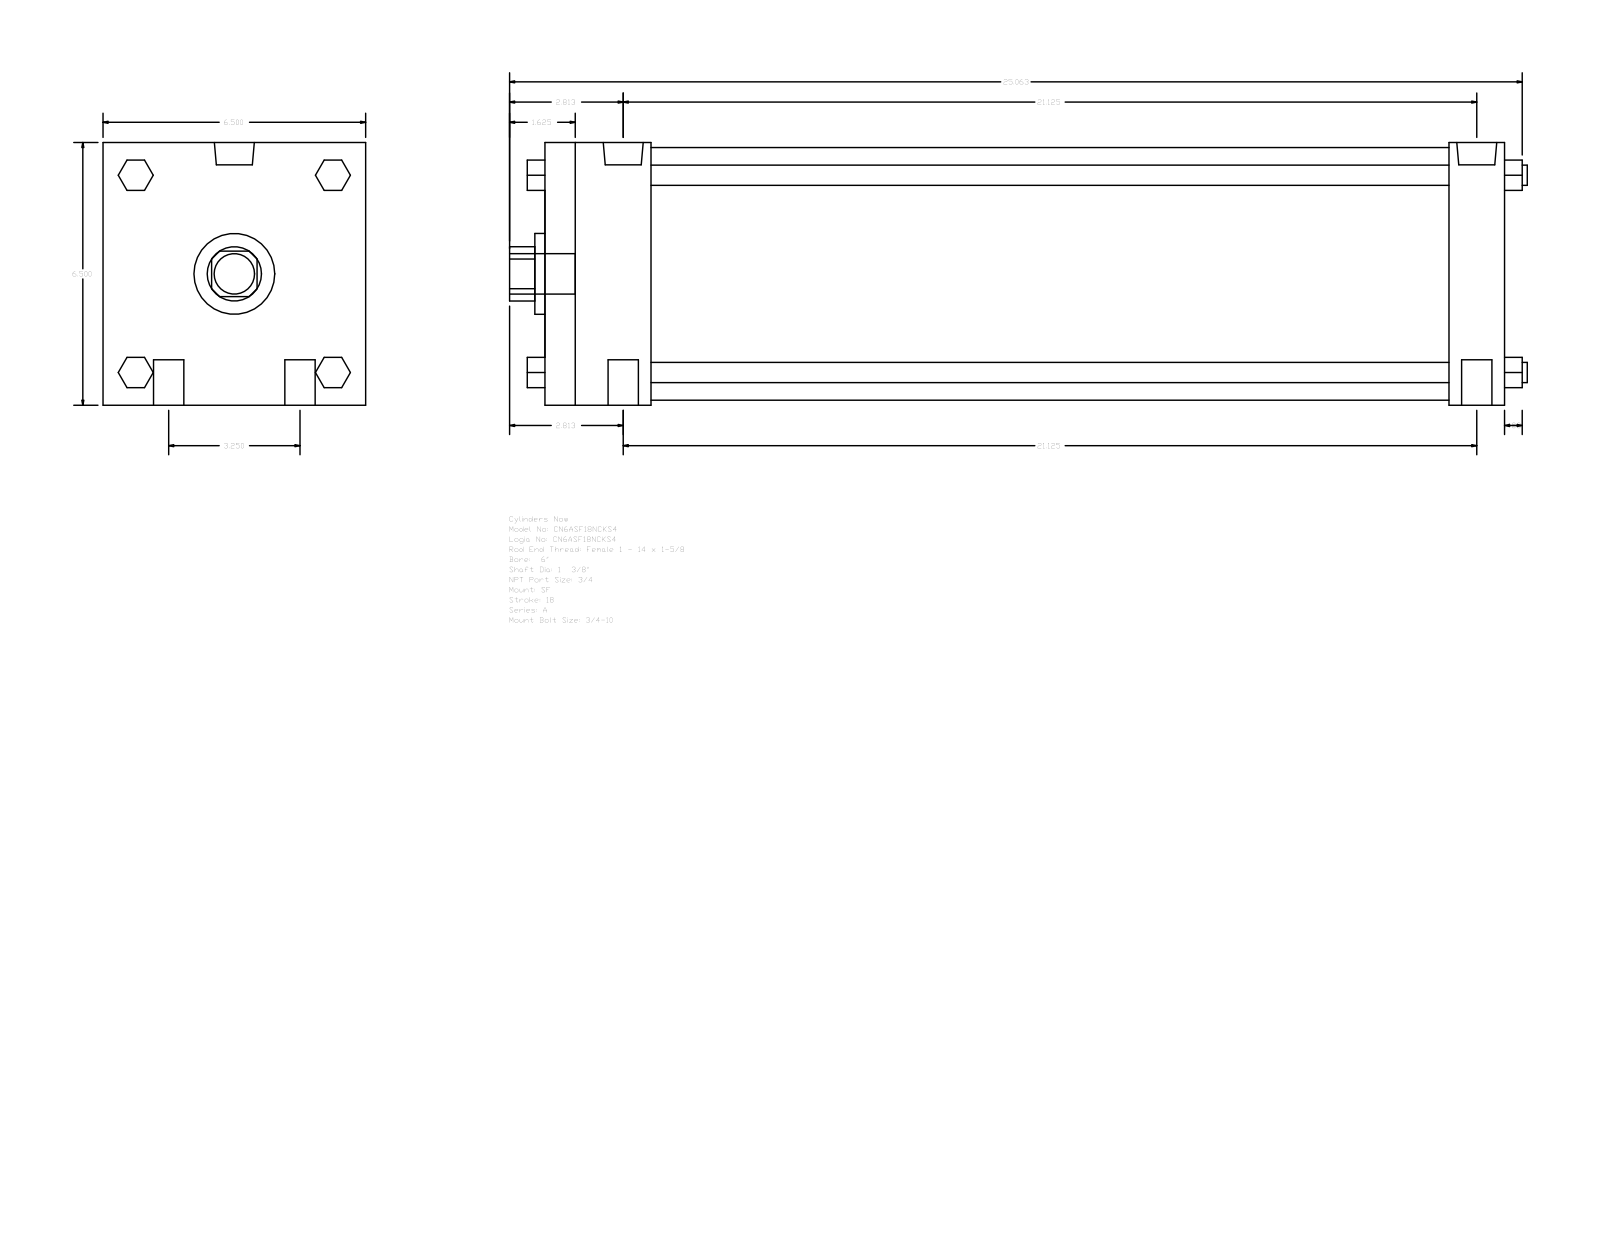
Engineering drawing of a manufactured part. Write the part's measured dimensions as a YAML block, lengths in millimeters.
part_name: "A_SF__0600_1.375"
step_written_by: "GSSL Pune (CONFIG_CONTROL_DESIGN)"
units: millimeters
bodies: {solids: 0, faces: 124, planar: 94, cylindrical: 30, other: 0}
overall_size: [639.76, 165.1, 165.1]
round_holes:
  - {diameter: 34.92, count: 1}
  - {diameter: 50.8, count: 1}
  - {diameter: 158.75, count: 1}
round_bosses_or_shafts:
  - {diameter: 19.05, count: 4}
  - {diameter: 12.7, count: 4}
  - {diameter: 25.12, count: 2}
  - {diameter: 15.08, count: 2}
  - {diameter: 25.4, count: 1}
partial_cylinders:
  - {radius: 17.06, count: 1}
face_to_face_distances: [165.1, 603.25, 568.32, 34.93, 66.67, 501.65, 536.58, 19.05, 61.97, 107.34]
